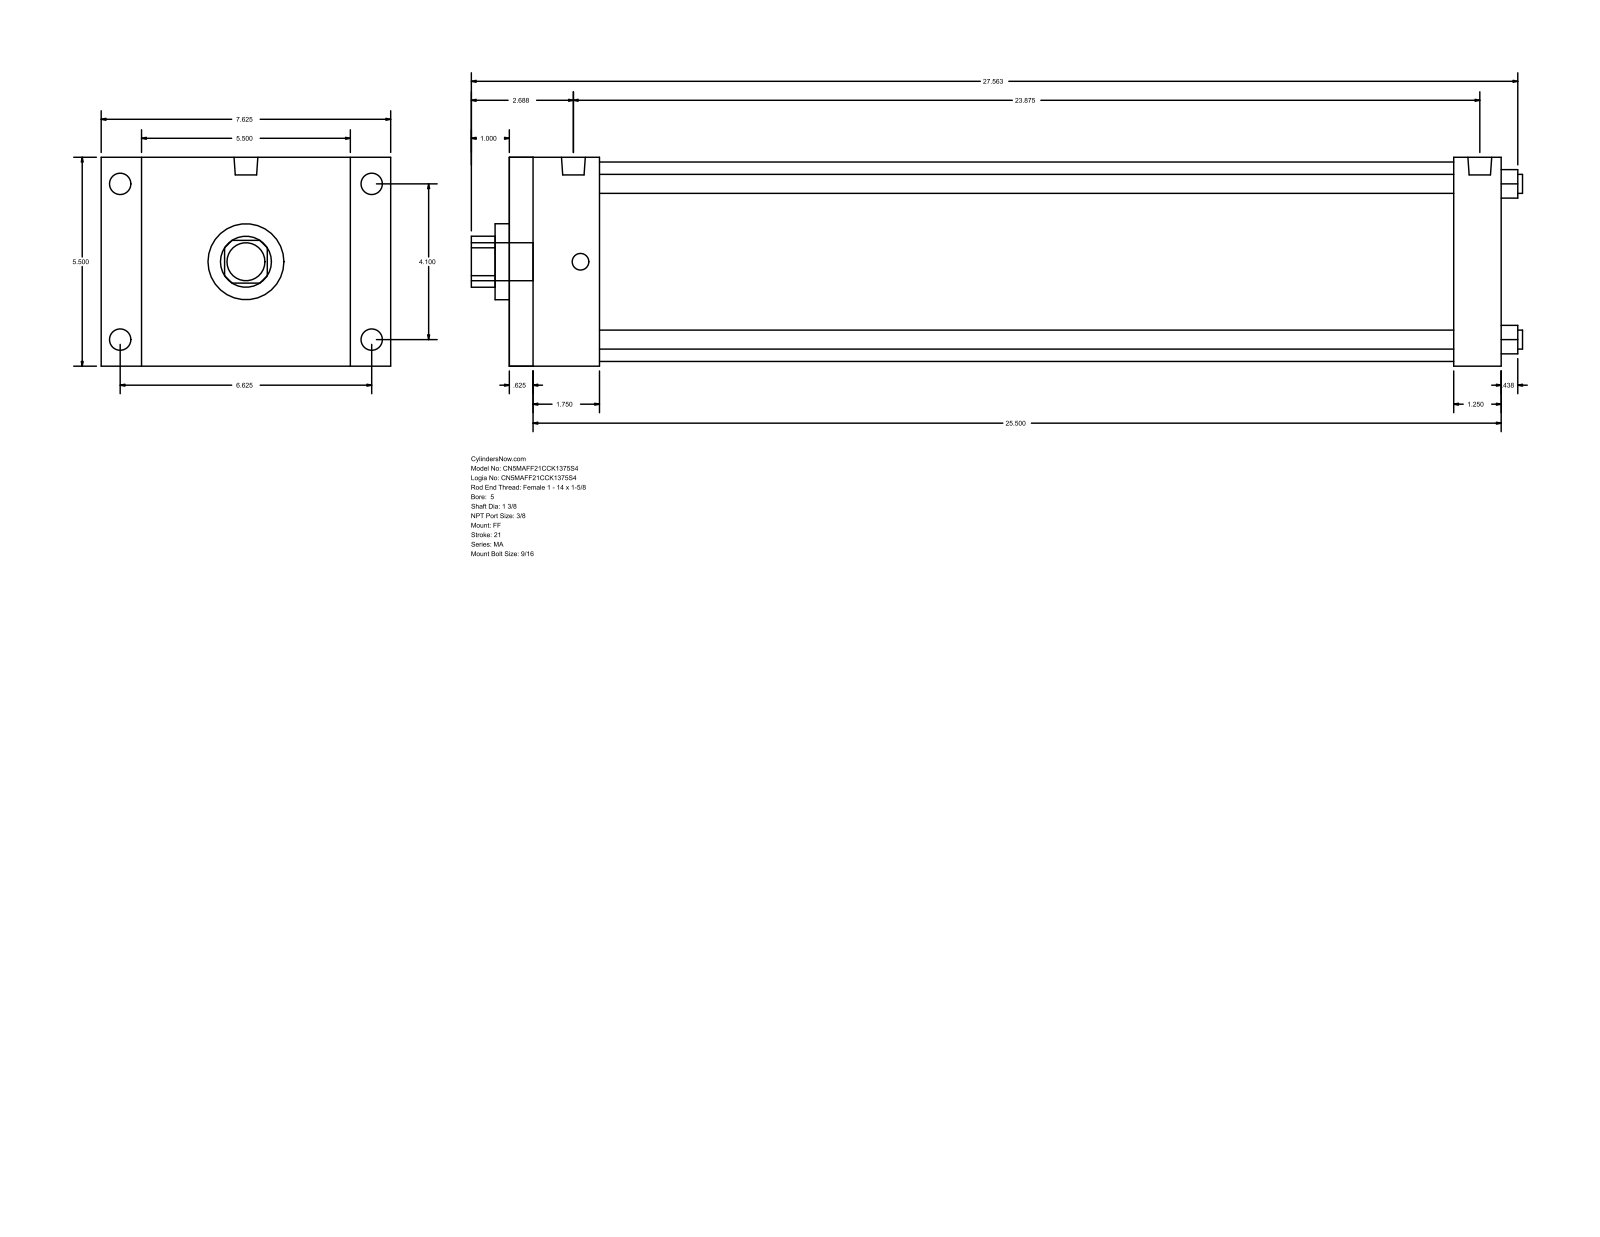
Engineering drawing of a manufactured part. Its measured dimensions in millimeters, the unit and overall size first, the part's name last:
Units: millimetres
Overall size (bounding box): 703.26 × 193.68 × 139.7
Round holes (diameter × count): ⌀12.7 ×4, ⌀34.92 ×1, ⌀50.8 ×1, ⌀133.35 ×1
Round bosses / shafts (diameter × count): ⌀14.29 ×4, ⌀11.11 ×4, ⌀15.93 ×2, ⌀25.4 ×1
Partial cylindrical surfaces — rounded edges, fillets, slot ends (radius × count): R17.06 ×1
Main face-to-face distances: 139.7, 663.58, 15.87, 647.71, 631.83, 615.96, 31.75, 60.32, 44.45, 571.51
Hole centre spacings: 73.64, 104.14, 147.28
Bodies: 0 solids, 92 faces (64 planar, 28 cylindrical, 0 other)
Part name (STEP PRODUCT): MA_FF__0500_1.375
STEP written by: GSSL Pune (CONFIG_CONTROL_DESIGN)
